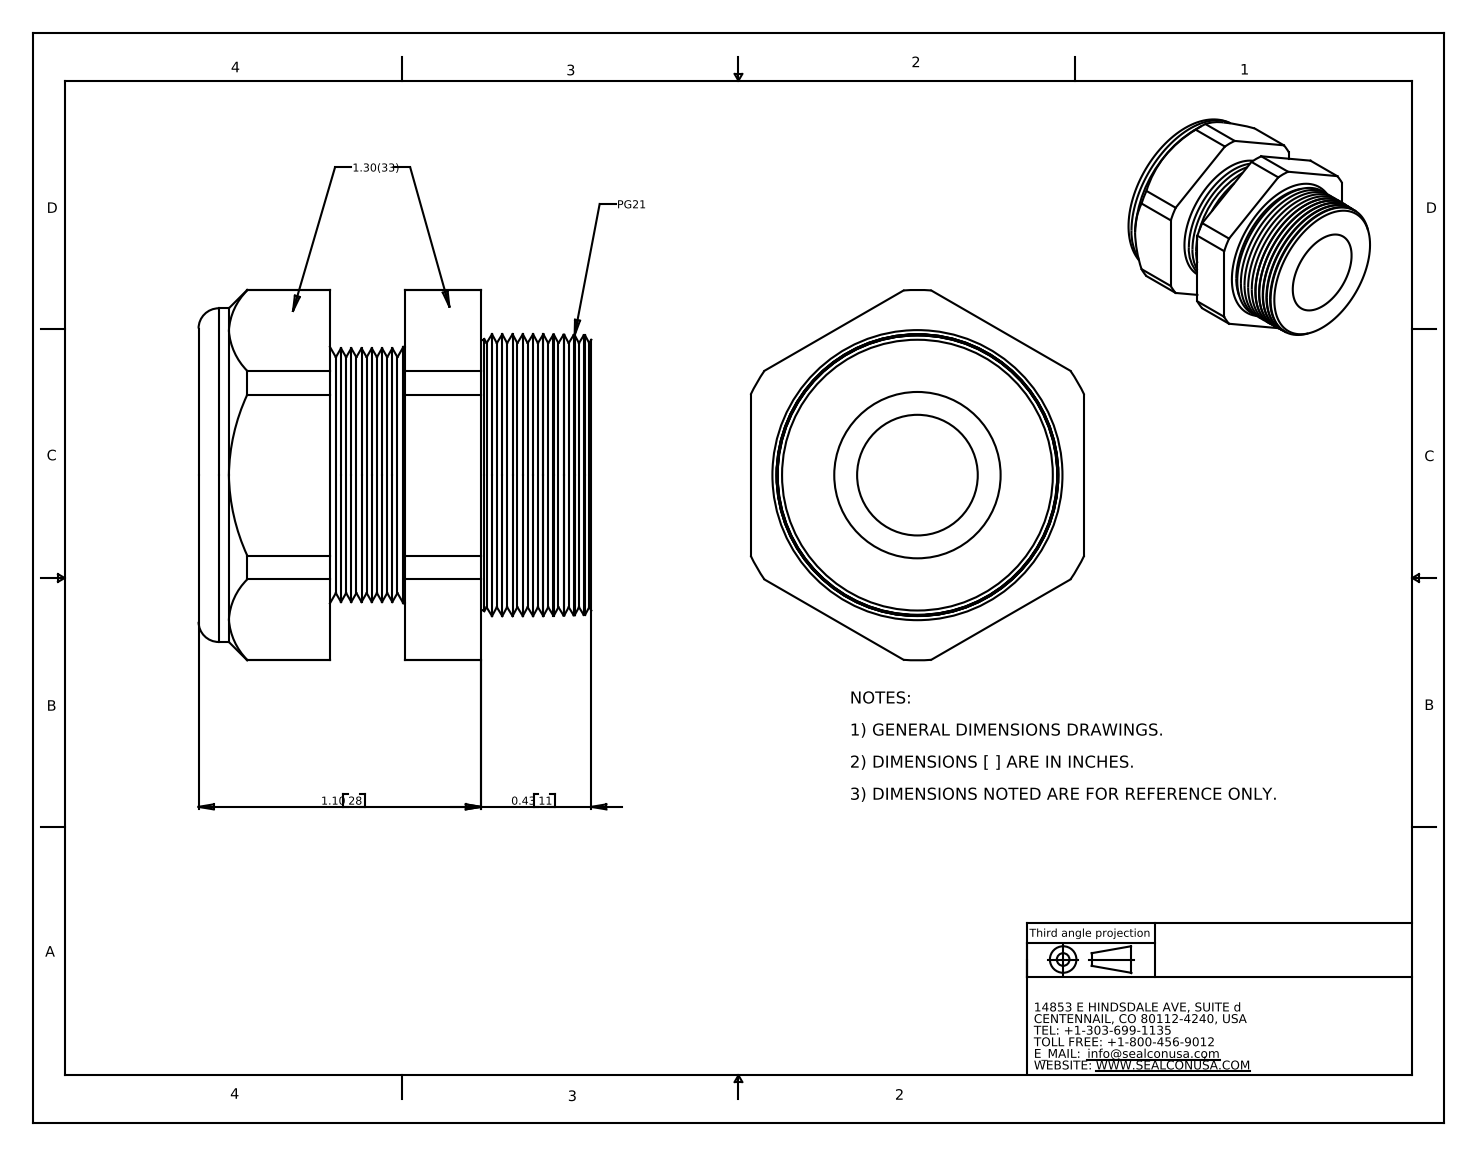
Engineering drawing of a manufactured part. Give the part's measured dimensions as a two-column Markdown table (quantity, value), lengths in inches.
| quantity | value |
| --- | --- |
| part name | CD21BR-BK |
| STEP written by | SolidWorks 2007 (CONFIG_CONTROL_DESIGN) |
| units | inches |
| bodies | 2 solids, 142 faces (20 planar, 24 cylindrical, 98 other) |
| overall size | 1.53 × 1.443 × 1.3 |
| volume | 1.407 in³ |
| surface area | 17.71 in² |
| round holes (diameter × count) | 0.47 × 1, 0.888 × 1 |
| round bosses / shafts (diameter × count) | 1.3 × 1, 0.999 × 1 |
| partial cylindrical surfaces (radius × count) | 0.721 × 1 |
| main face-to-face distances | 1.3, 0.293, 1.018, 0.725, 0.588, 0.295, 0.43, 0.512, 0.805, 1.1 |
